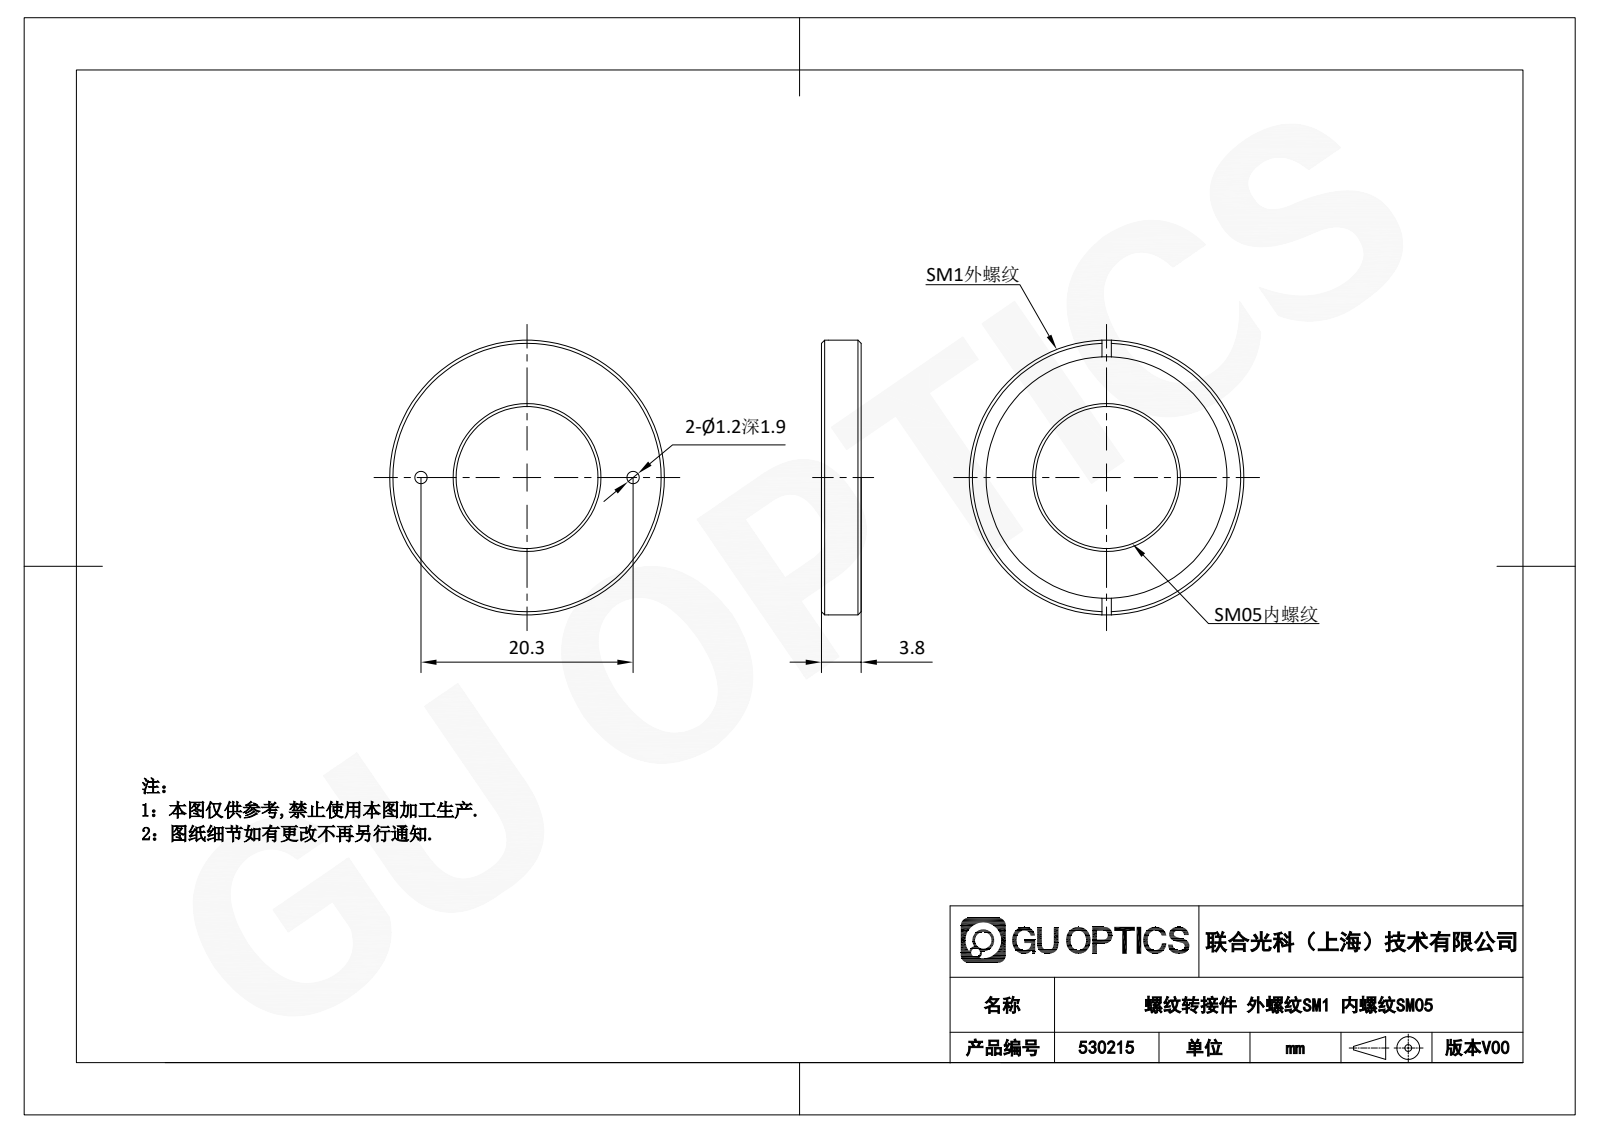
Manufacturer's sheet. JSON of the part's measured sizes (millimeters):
{"part_name": "530215", "step_written_by": "SolidWorks 2020 (CONFIG_CONTROL_DESIGN)", "units": "millimeters", "bodies": {"solids": 1, "faces": 22, "planar": 12, "cylindrical": 5, "other": 5}, "overall_size": [26.29, 26.29, 3.8], "volume_mm3": 1275, "surface_area_mm2": 1268, "round_holes": [[1.2, 2], [13.59, 1], [23.1, 1]], "round_bosses_or_shafts": [[26.29, 1]], "face_to_face_distances": [3, 3.8, 0.8, 1.9, 3.15, 0.65, 1.1, 1.25, 0.9], "hole_center_spacings": [10.15, 20.3]}
